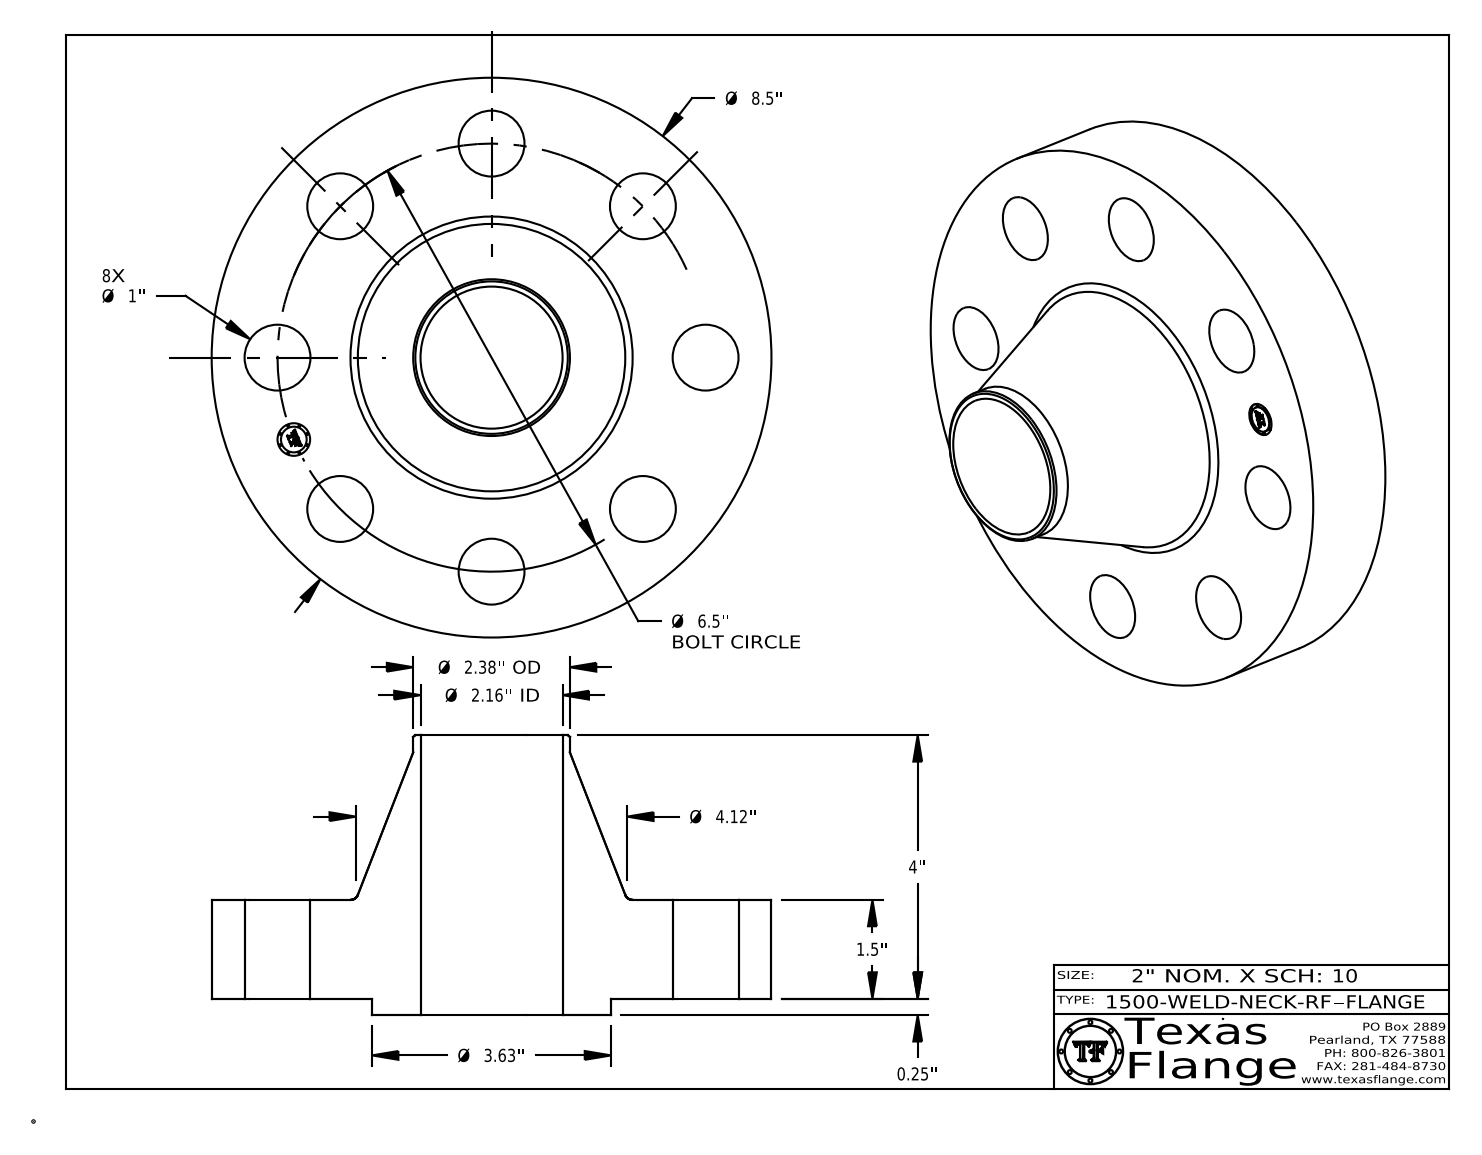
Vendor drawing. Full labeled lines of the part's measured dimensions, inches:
Part name (STEP PRODUCT): 1500-WELD-NECK-RF
STEP written by: CATIA V5 STEP AP214 (AUTOMOTIVE_DESIGN)
Units: inches
Bodies: 1 solid, 419 faces (369 planar, 44 cylindrical, 6 other)
Overall size (bounding box): 8.5 × 8.5 × 4.25
Volume: 82.94 in³ · Surface area: 220.3 in²
Round holes (diameter × count): ⌀1 ×8, ⌀0.495 ×1, ⌀2.157 ×1
Round bosses / shafts (diameter × count): ⌀0.03 ×8, ⌀8.5 ×1, ⌀3.63 ×1, ⌀2.38 ×1, ⌀0.39 ×1
Main face-to-face distances: 1.5, 0.25, 1.75, 4.25, 4, 2.5, 1.735, 1.485, 0.015, 2.515
Hole centre spacings: 3.25, 2.487, 4.596, 6.005, 6.5, 1.268, 5.405, 6.375
